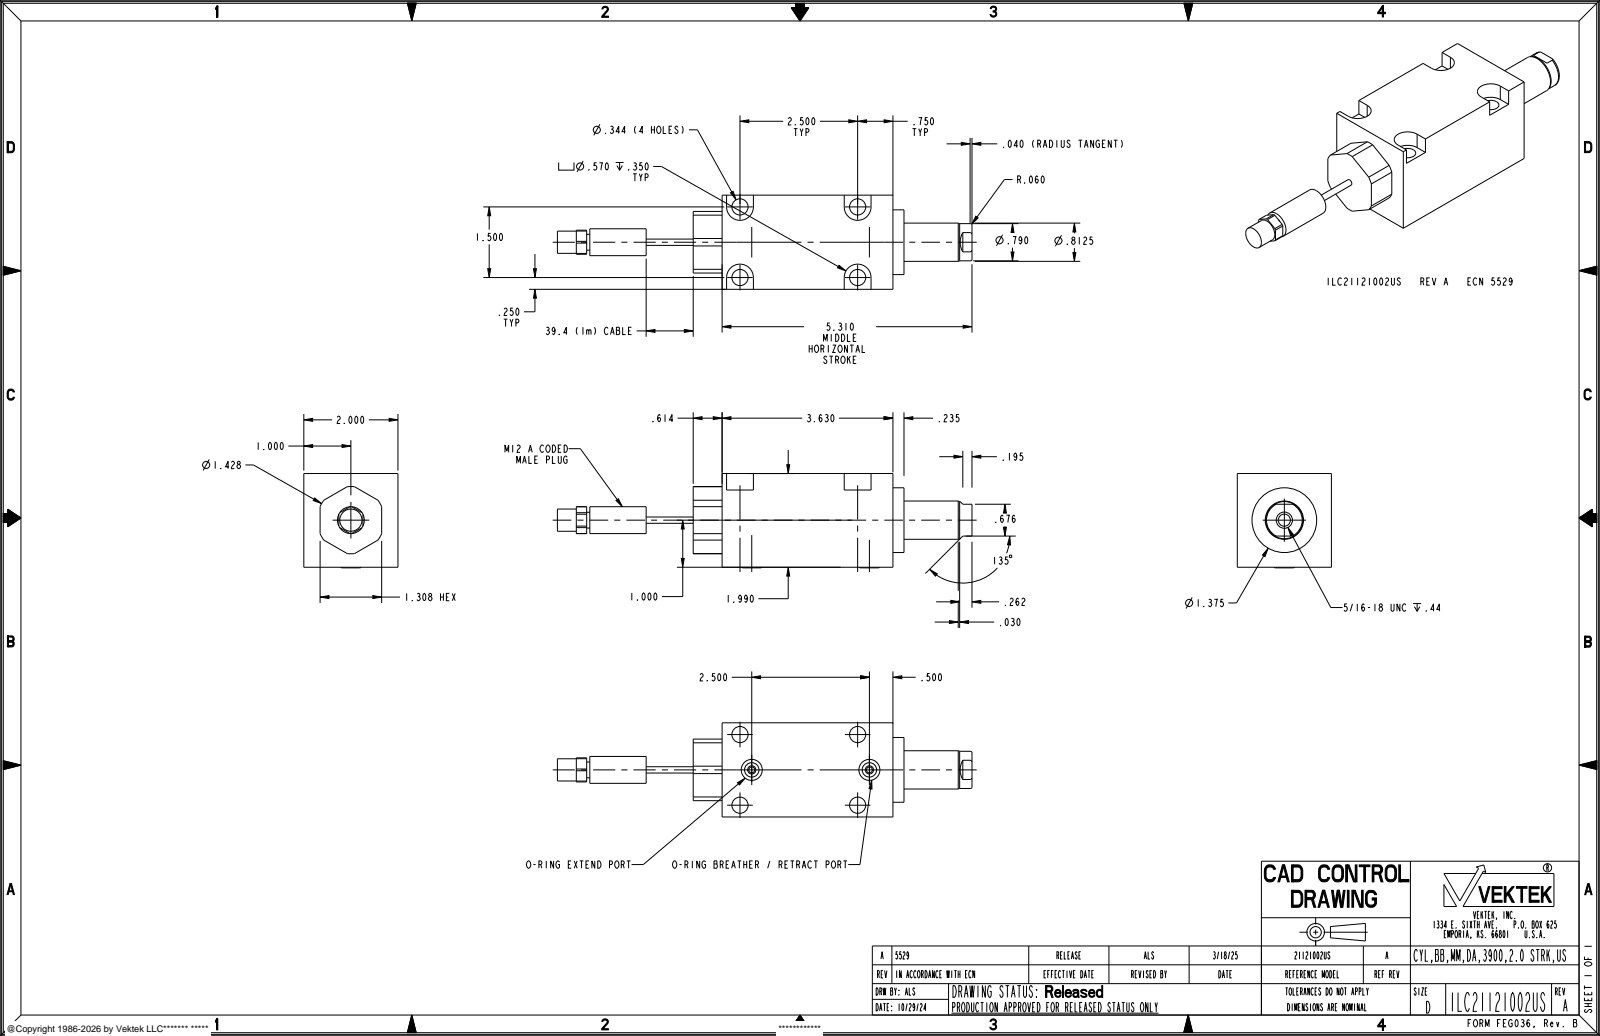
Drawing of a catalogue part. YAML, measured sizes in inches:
part_name: "ILC21121002US"
step_written_by: "CREO PARAMETRIC BY PTC INC, 2021164 (AUTOMOTIVE_DESIGN)"
units: inches
bodies: {solids: 1, faces: 120, planar: 46, cylindrical: 52, other: 22}
overall_size: [8.81, 2.2, 2.003]
volume: 15.84
surface_area: 58.02
round_holes:
  - {diameter: 0.344, count: 4}
  - {diameter: 0.125, count: 2}
  - {diameter: 0.447, count: 2}
  - {diameter: 0.257, count: 1}
round_bosses_or_shafts:
  - {diameter: 1.375, count: 1}
  - {diameter: 0.813, count: 1}
  - {diameter: 0.79, count: 1}
  - {diameter: 0.571, count: 1}
  - {diameter: 0.472, count: 1}
  - {diameter: 0.335, count: 1}
  - {diameter: 0.312, count: 1}
  - {diameter: 0.134, count: 1}
partial_cylinders:
  - {radius: 0.285, count: 4}
  - {radius: 0.714, count: 1}
face_to_face_distances: [2, 1.99, 3.63, 4.244, 0.614, 1.308, 0.235, 3.865, 4.479, 1.64]
hole_center_spacings: [0.791, 2.5, 1.5, 2.372, 2.85, 2.915]
